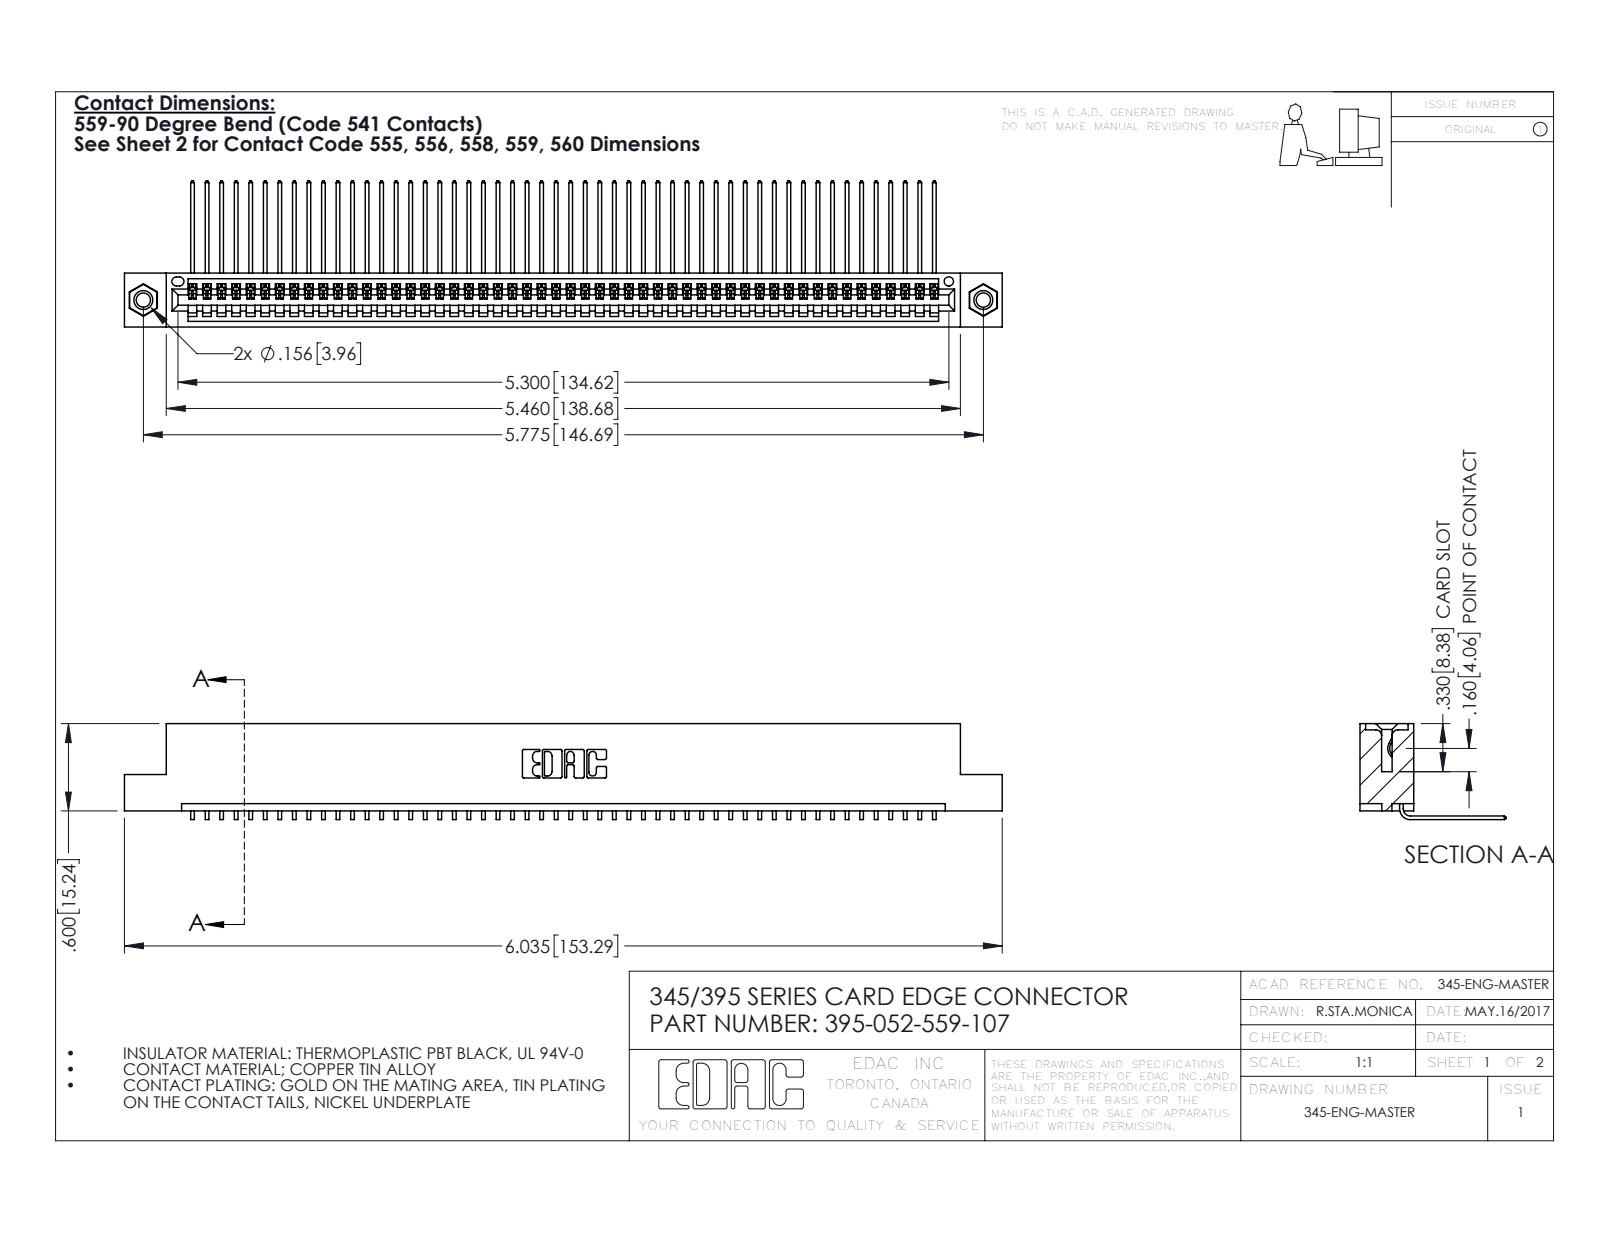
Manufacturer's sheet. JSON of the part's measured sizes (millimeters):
{"part_name": "345 Part_Flush Mounting Lugs - 0.156 Dia-TI; 345-250-001_345-250-005-103; 345-292-001_558 559 Tail - 1; 395-052-559-107", "step_written_by": "SolidWorks 2016 (CONFIG_CONTROL_DESIGN)", "units": "millimeters", "bodies": {"solids": 55, "faces": 3306, "planar": 2296, "cylindrical": 994, "other": 16}, "overall_size": [153.3, 25.5, 16.7], "volume_mm3": 14800, "surface_area_mm2": 20860, "round_holes": [[2.5, 2], [3.2, 2], [4, 2], [1.6, 1]], "round_bosses_or_shafts": [[3.9, 2]], "partial_cylinders_radius": [[0.2, 104], [0.3, 22], [0.2, 6], [0.8, 6], [0.7, 3], [0.8, 2], [1, 2], [0.4, 1]], "face_to_face_distances": [1.8, 7.6, 9.4, 5.1, 2.5, 6.9, 0.6, 5.7, 3.8, 1.8], "hole_center_spacings": [6.9, 140.7, 146.7]}
